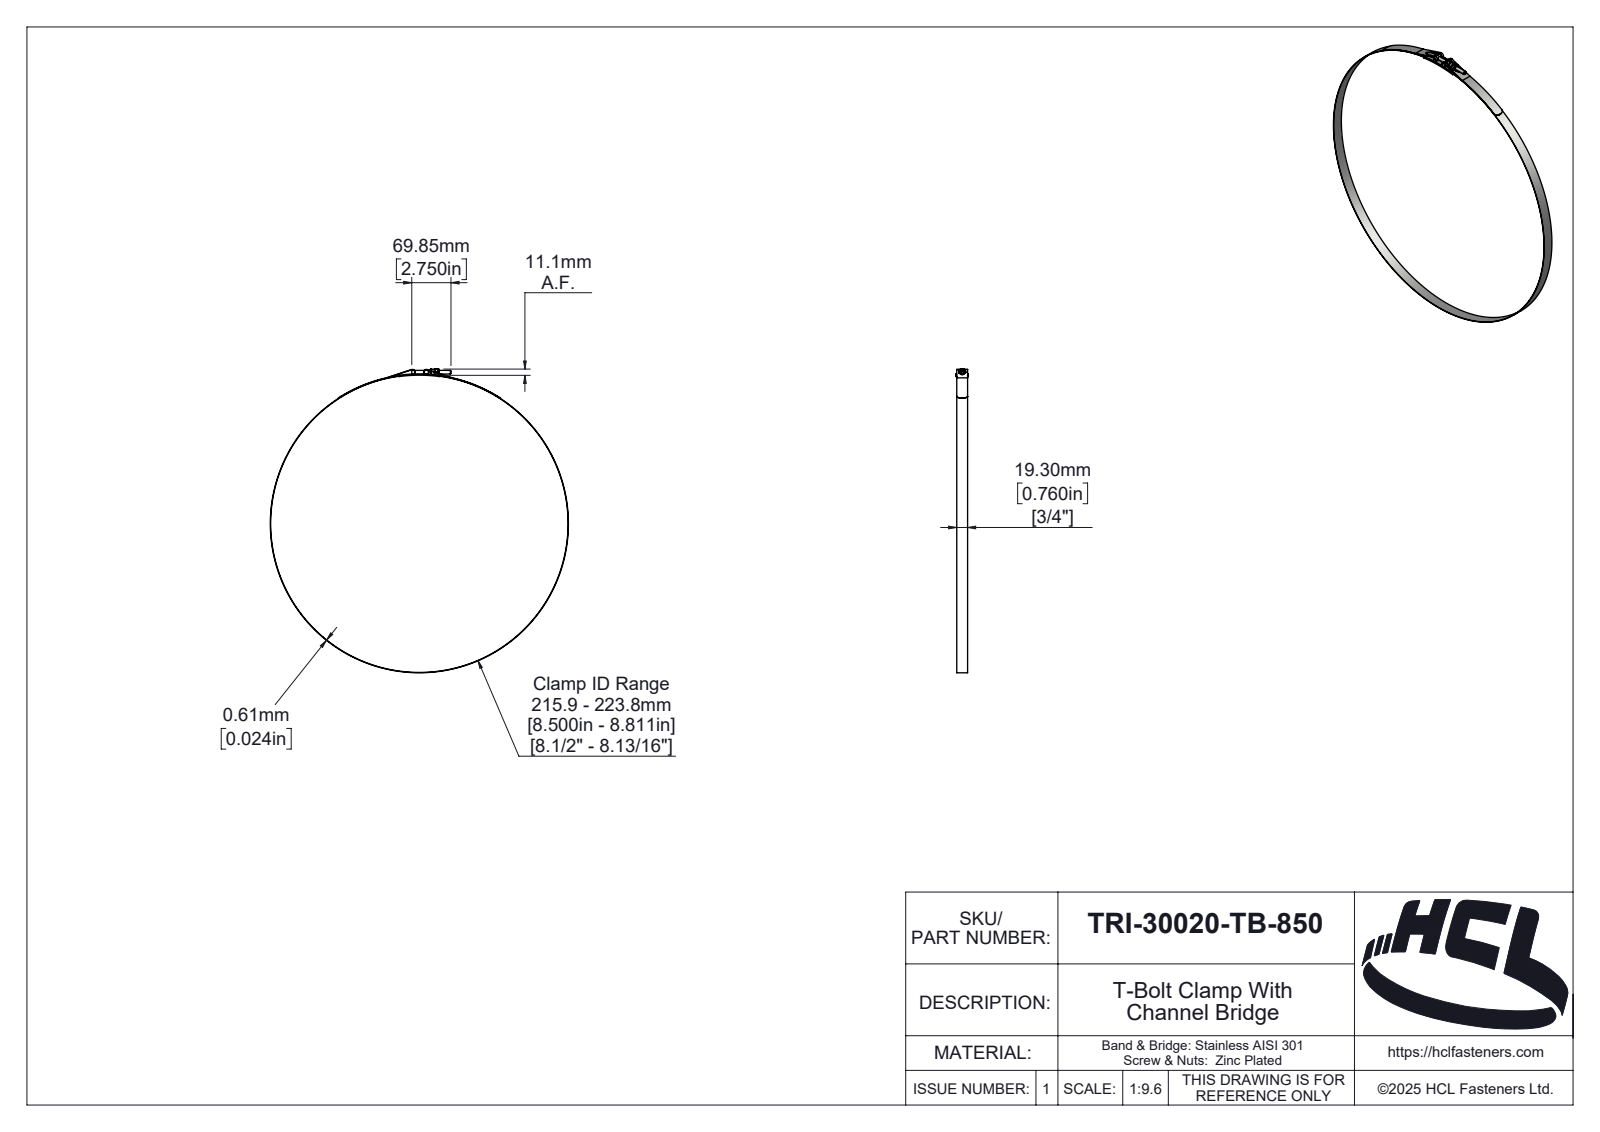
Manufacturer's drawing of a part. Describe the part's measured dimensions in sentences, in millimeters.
The part is named "TRI-30020-TB-850". Its 3-D file was written by "SolidWorks 2025 (AUTOMOTIVE_DESIGN)". It is 6 solids with 330 faces: 44 planar, 122 cylindrical and 164 other. Overall it measures 541.04 by 531.22 by 22 millimeters. Its volume is 27 790 cubic millimeters and its surface area 84 380 square millimeters. Round holes: 1 of diameter 5.4, 1 of diameter 6.35, 1 of diameter 6.5, 1 of diameter 7.58, 1 of diameter 530. Round bosses or shafts: 2 of diameter 8.58, 1 of diameter 531.22, 1 of diameter 10.58. Partial cylindrical surfaces (rounded edges, fillets, slot ends): 6 of radius 0.39, 2 of radius 0.5, 2 of radius 4.39, 2 of radius 5, 1 of radius 0.59, 1 of radius 2.42, 1 of radius 3.03, 1 of radius 3.19. The main face-to-face distances are 0.61, 19.3, 1.35, 20.65, 0.74, 21.39, 20.04, 22, 20.78, 41. The hole center spacings are 270.
